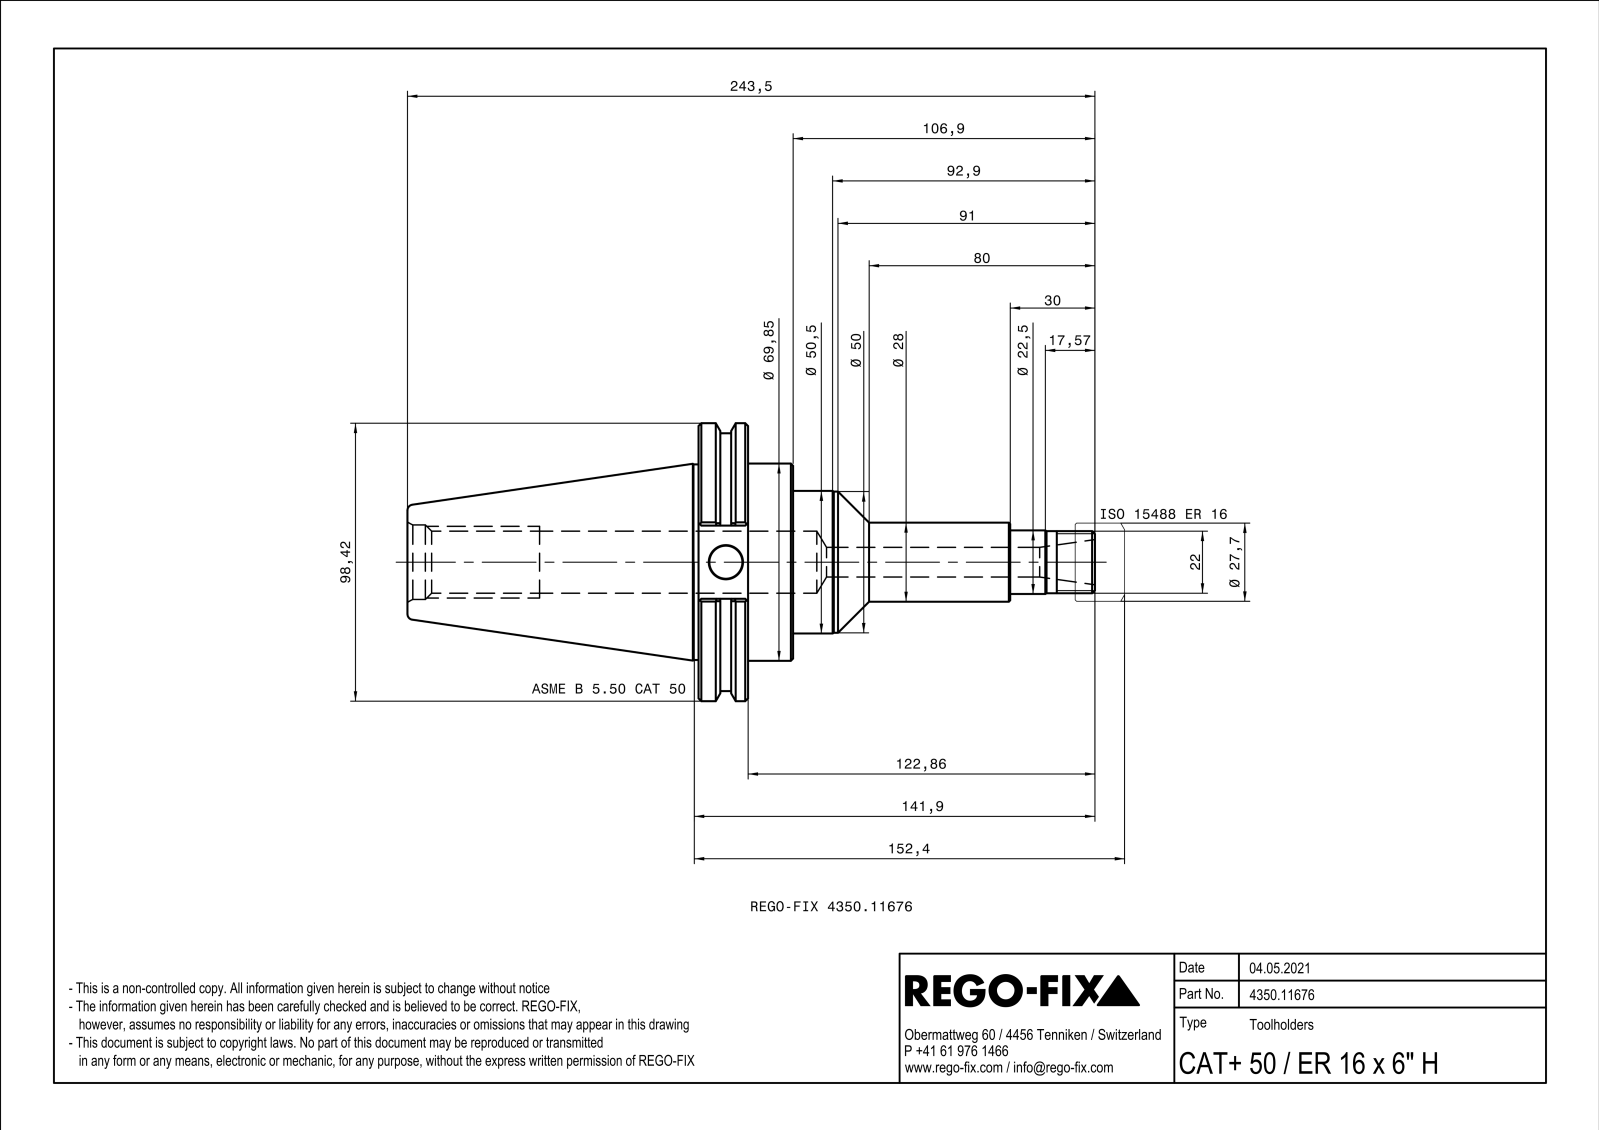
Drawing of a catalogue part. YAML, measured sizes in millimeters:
part_name: "NOCUT"
step_written_by: "SIEMENS PLM Software Solid Edge ST10 (AUTOMOTIVE_DESIGN)"
units: millimeters
bodies: {solids: 2, faces: 280, planar: 104, cylindrical: 67, other: 109}
overall_size: [243.9, 98.72, 94.65]
volume: 901301
surface_area: 127874
round_holes:
  - {diameter: 3.9, count: 2}
  - {diameter: 4.5, count: 2}
  - {diameter: 3.24, count: 1}
  - {diameter: 10.5, count: 1}
  - {diameter: 12, count: 1}
  - {diameter: 21.96, count: 1}
  - {diameter: 21.96, count: 1}
  - {diameter: 26.1, count: 1}
  - {diameter: 26.4, count: 1}
round_bosses_or_shafts:
  - {diameter: 98.72, count: 1}
  - {diameter: 98.43, count: 1}
  - {diameter: 91.3, count: 1}
  - {diameter: 70.15, count: 1}
  - {diameter: 69.85, count: 1}
  - {diameter: 69.25, count: 1}
  - {diameter: 50.8, count: 1}
  - {diameter: 50.5, count: 1}
partial_cylinders:
  - {radius: 0.5, count: 4}
face_to_face_distances: [33.75, 17.55, 17.75, 16, 33.55, 16.2, 33.95, 136.85, 103.1, 72.73]
